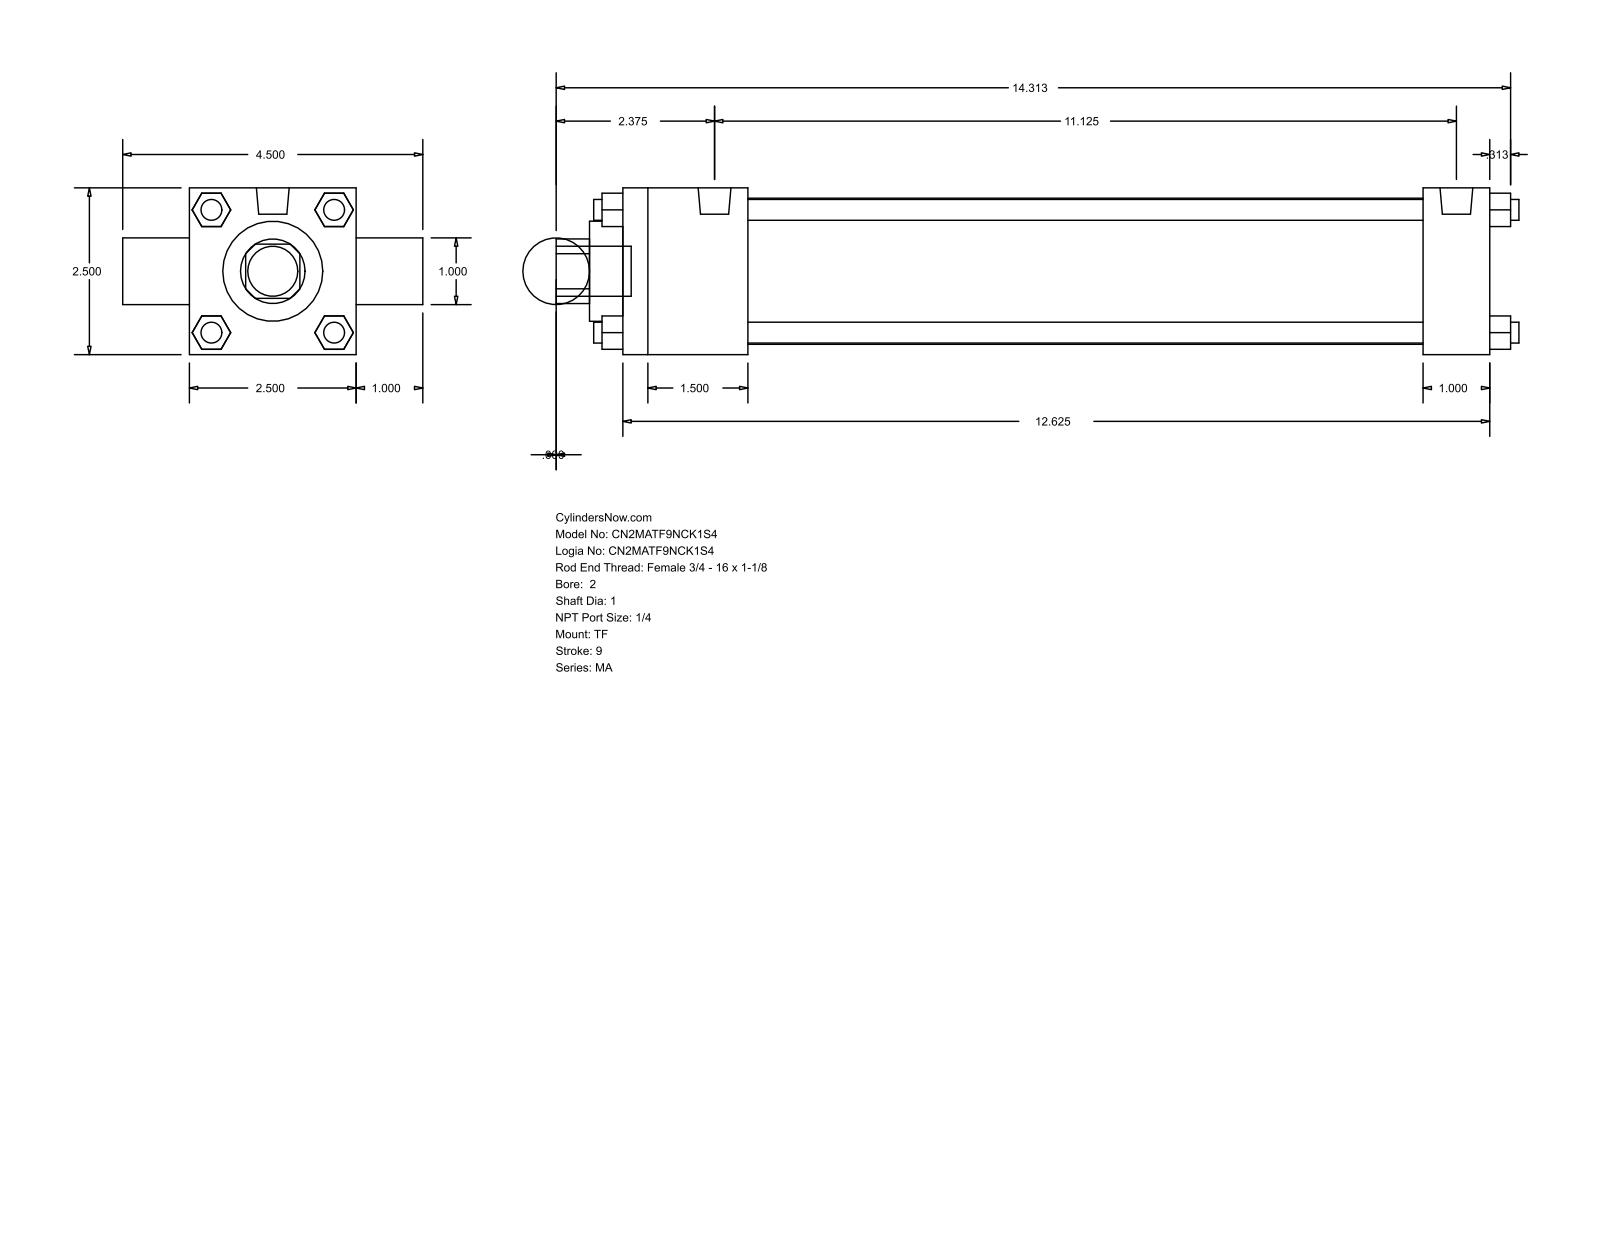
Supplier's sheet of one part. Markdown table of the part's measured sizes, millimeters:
| quantity | value |
| --- | --- |
| part name | MA_TF__0200_1 |
| STEP written by | GSSL Pune (CONFIG_CONTROL_DESIGN) |
| units | millimeters |
| bodies | 0 solids, 120 faces (92 planar, 28 cylindrical, 0 other) |
| overall size | 366.71 × 114.3 × 63.5 |
| round holes (diameter × count) | 25.4 × 2, 38.1 × 1, 55.63 × 1 |
| round bosses / shafts (diameter × count) | 7.94 × 7, 12.49 × 2, 19.05 × 1 |
| partial cylindrical surfaces (radius × count) | 12.29 × 1 |
| main face-to-face distances | 63.5, 25.4, 330.2, 12.7, 47.63, 304.8, 257.17, 282.57, 88.9, 23.37 |
